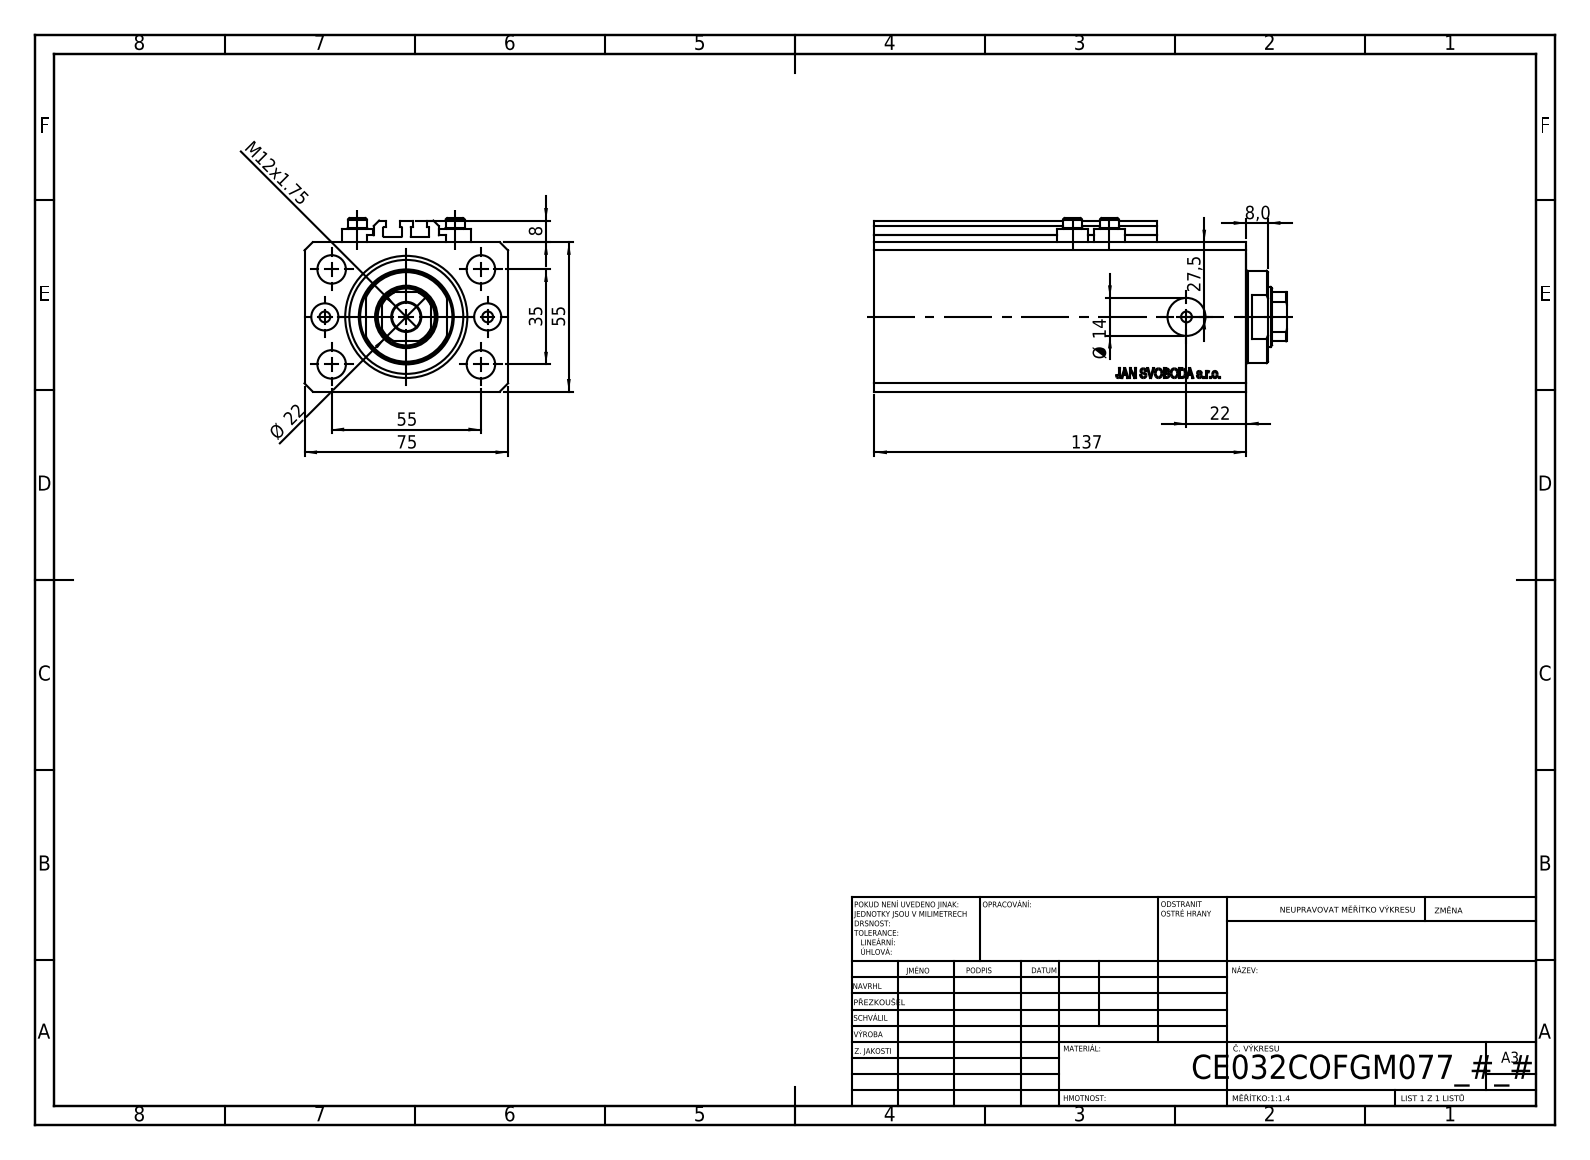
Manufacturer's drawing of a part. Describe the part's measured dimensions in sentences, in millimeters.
The part is named "V250CE_C_Body; ALLEN BOLT V250CE; V250CE_VC_C; V250CE_C_VCP". Its 3-D file was written by "SolidWorks 2019 (CONFIG_CONTROL_DESIGN)". It is 8 solids with 1034 faces: 504 planar, 86 cylindrical and 444 other. Overall it measures 152 by 75 by 64 millimeters. Its volume is 502 424 cubic millimeters and its surface area 108 812 square millimeters. Round holes: 8 of diameter 4, 5 of diameter 10.5, 2 of diameter 10, 2 of diameter 14, 1 of diameter 22, 1 of diameter 32, 1 of diameter 45. Round bosses or shafts: 4 of diameter 11.6, 4 of diameter 7, 1 of diameter 34. Partial cylindrical surfaces (rounded edges, fillets, slot ends): 10 of radius 0.2, 1 of radius 10.5. The main face-to-face distances are 55, 75, 137, 15, 122, 9.9, 112.1, 127.1, 2.5, 2. The hole center spacings are 17.68, 32.6, 60.1, 13.6, 30, 35, 36, 38.48.
